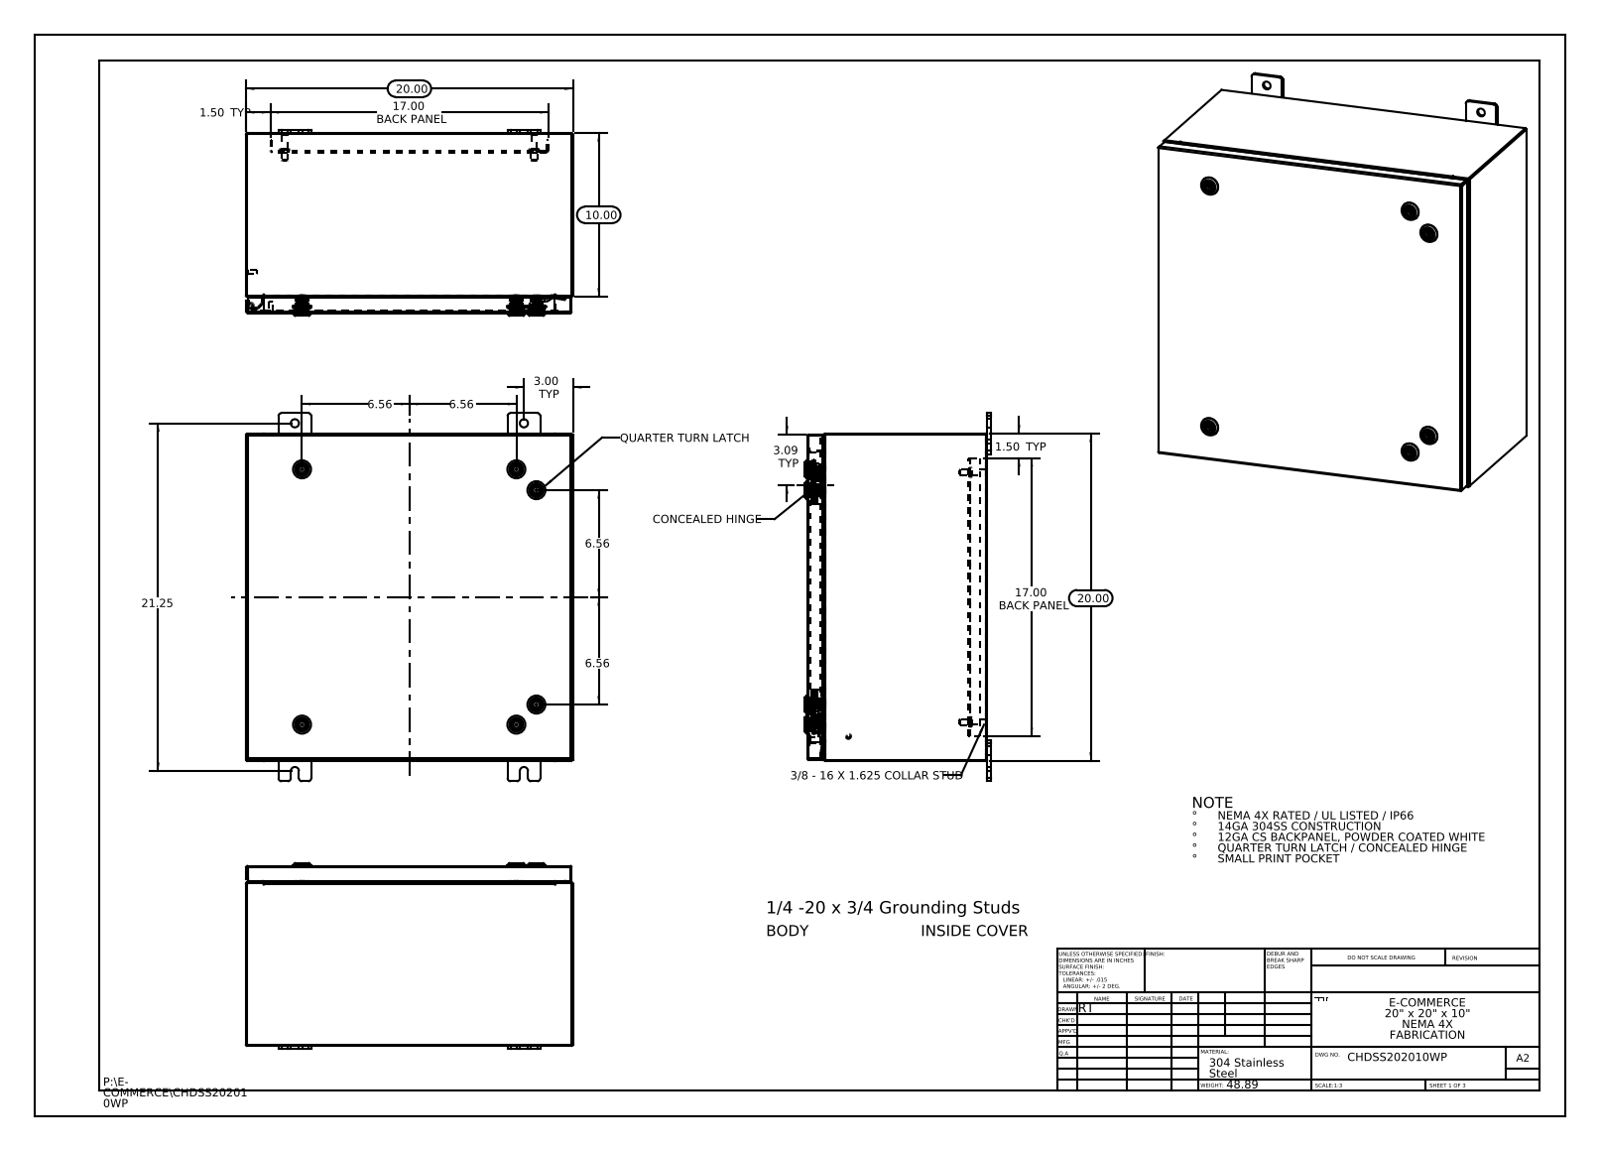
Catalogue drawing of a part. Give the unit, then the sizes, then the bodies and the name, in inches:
Units: inches
Overall size (bounding box): 22.5 × 20 × 11.356
Round holes (diameter × count): ⌀0.5 ×8, ⌀0.197 ×6, ⌀0.394 ×6, ⌀0.4 ×6, ⌀0.63 ×6, ⌀0.787 ×6, ⌀0.136 ×4, ⌀0.211 ×1
Round bosses / shafts (diameter × count): ⌀0.236 ×8, ⌀1.102 ×6, ⌀0.78 ×6, ⌀0.626 ×6, ⌀0.61 ×6, ⌀0.531 ×6, ⌀0.392 ×6, ⌀0.114 ×6
Partial cylindrical surfaces — rounded edges, fillets, slot ends (radius × count): R0.006 ×198, R0.118 ×198, R0.028 ×72, R0.02 ×24, R0.19 ×24, R0.197 ×22, R0.013 ×20, R0.088 ×18
Main face-to-face distances: 0.075, 19.925, 0.074, 19.85, 20, 11.01, 10.935, 10.936, 10.861, 0.104
Hole centre spacings: 13.1, 0.688, 1.858, 3.065, 13.687, 14, 14.378, 15.25
Volume: 175.1 in³ · Surface area: 4 406 in²
Bodies: 55 solids, 5420 faces (1592 planar, 1692 cylindrical, 2136 other)
Part name (STEP PRODUCT): HW-CLH-E5-8004_Cam-232112-U-Industrilas; CHDSS202010WP Body; Concealed Hinge (Cover Side); Washer-221320-IB-Industrilas_Washer-221320-IB-Industrilas (+8 more)
STEP written by: SolidWorks 2013 (CONFIG_CONTROL_DESIGN)
